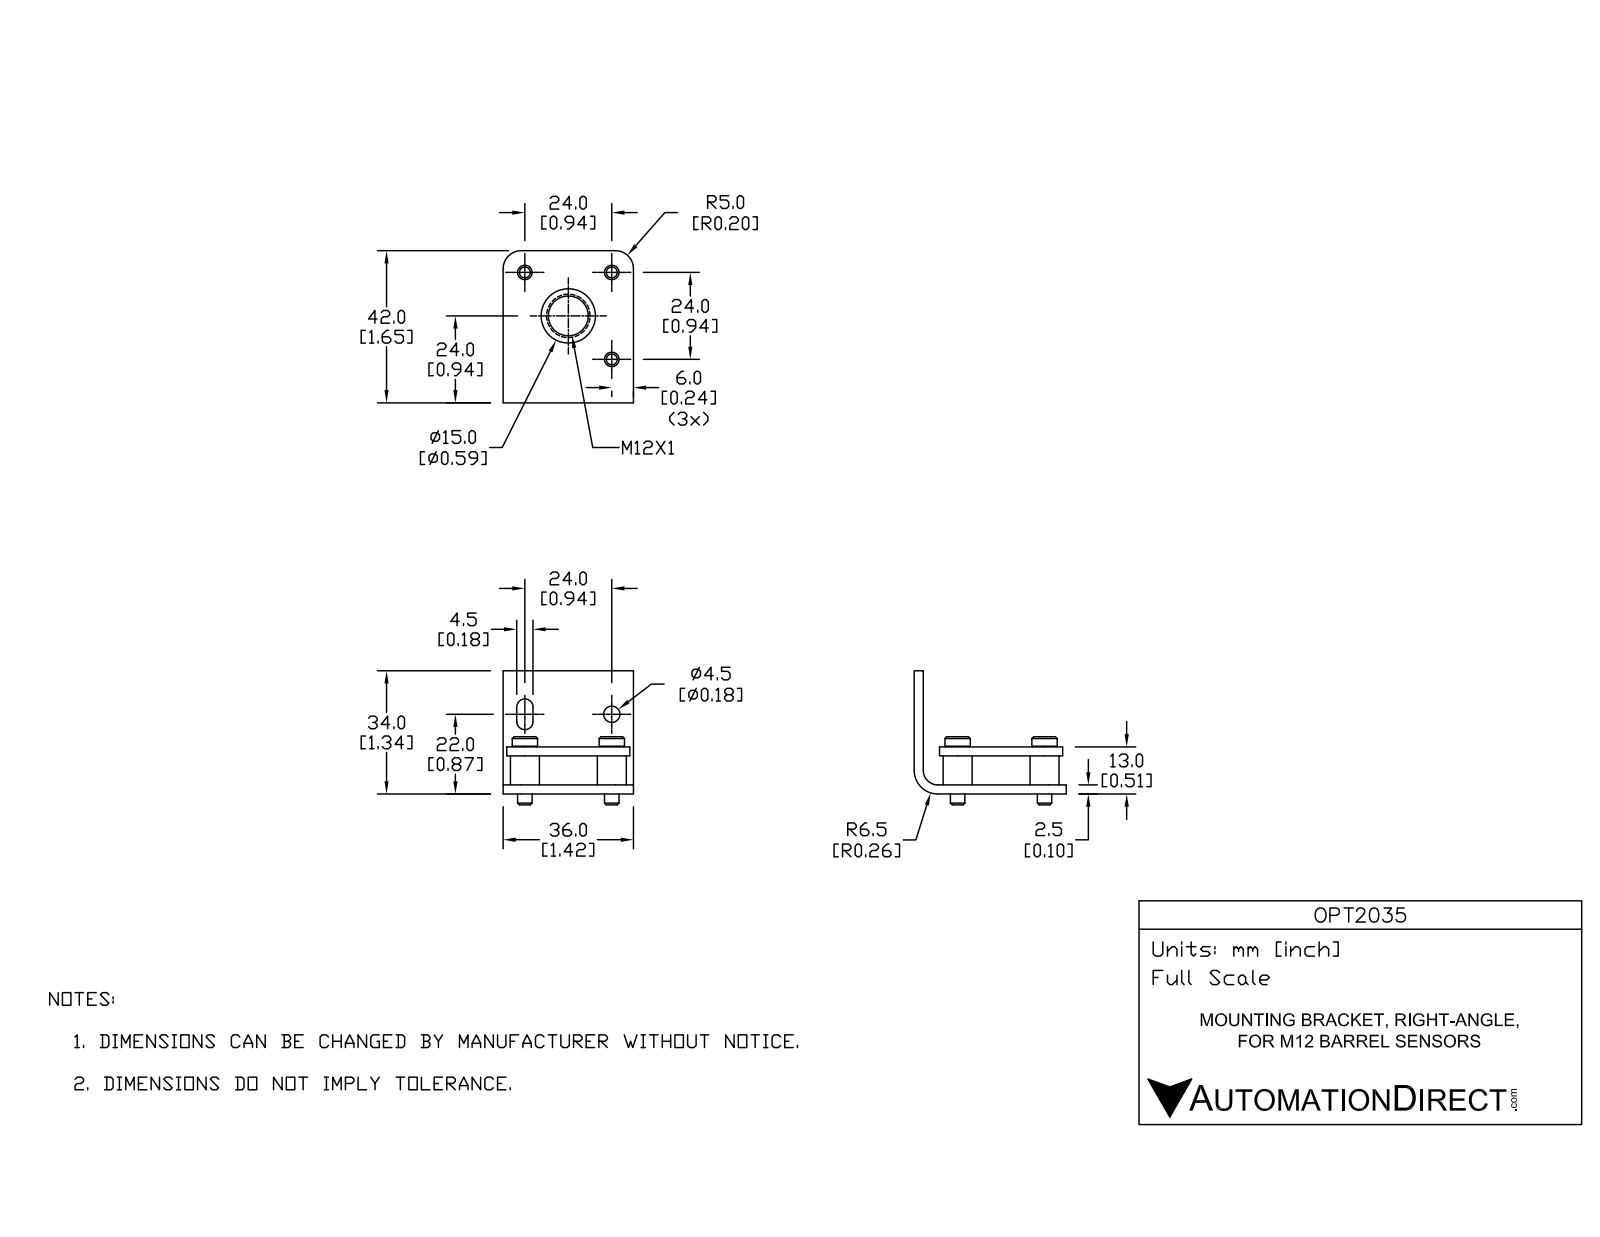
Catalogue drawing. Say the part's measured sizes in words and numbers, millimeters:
Its 3-D file was written by "Unknown (CONFIG_CONTROL_DESIGN)". It is 1 solid with 92 faces: 52 planar, 31 cylindrical and 9 other. Overall it measures 42 by 37 by 36 millimeters. Its volume is 9 697 cubic millimeters and its surface area 9 512 square millimeters. Round holes: 4 of diameter 4.5, 3 of diameter 5.6, 1 of diameter 11, 1 of diameter 15. Round bosses or shafts: 3 of diameter 8, 3 of diameter 7, 3 of diameter 4. Partial cylindrical surfaces (rounded edges, fillets, slot ends): 6 of radius 5, 2 of radius 2.25, 1 of radius 4, 1 of radius 6.5. The main face-to-face distances are 2.5, 10.5, 13, 8, 34, 35, 1, 36, 31.5, 23.5. The hole center spacings are 16.97, 24, 33.94.
